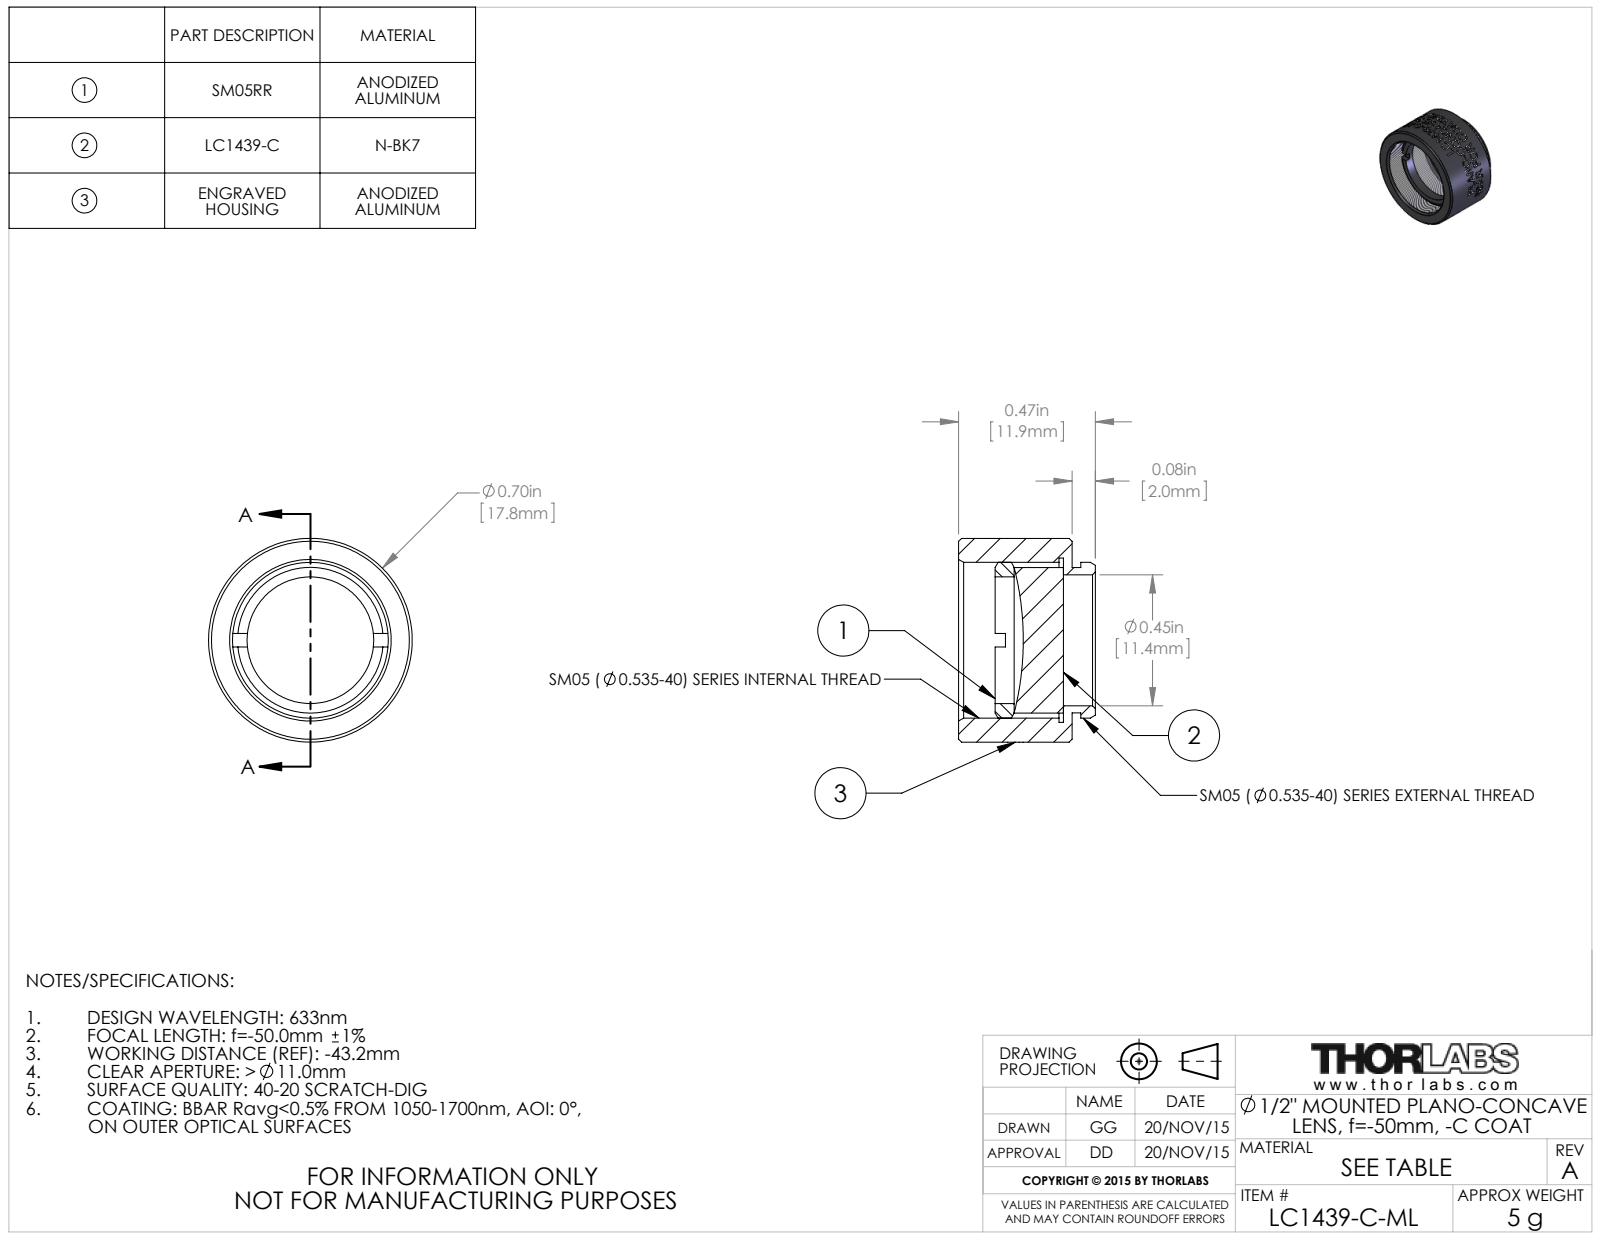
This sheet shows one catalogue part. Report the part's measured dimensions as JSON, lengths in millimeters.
{"part_name": "TTN045269-E0W", "step_written_by": "SolidWorks 2014 (CONFIG_CONTROL_DESIGN)", "units": "millimeters", "bodies": {"solids": 3, "faces": 151, "planar": 16, "cylindrical": 118, "other": 17}, "overall_size": [17.8, 17.8, 11.9], "volume_mm3": 1670, "surface_area_mm2": 2092, "round_holes": [[11, 1], [11.4, 1], [13.6, 1], [14.4, 1]], "round_bosses_or_shafts": [[17.8, 1], [13.6, 1], [12.7, 1], [12.7, 1]], "face_to_face_distances": [0.8, 9.9, 9.1, 5.1, 4.3, 4.9, 6.7, 5.9, 1.7, 3.2]}
